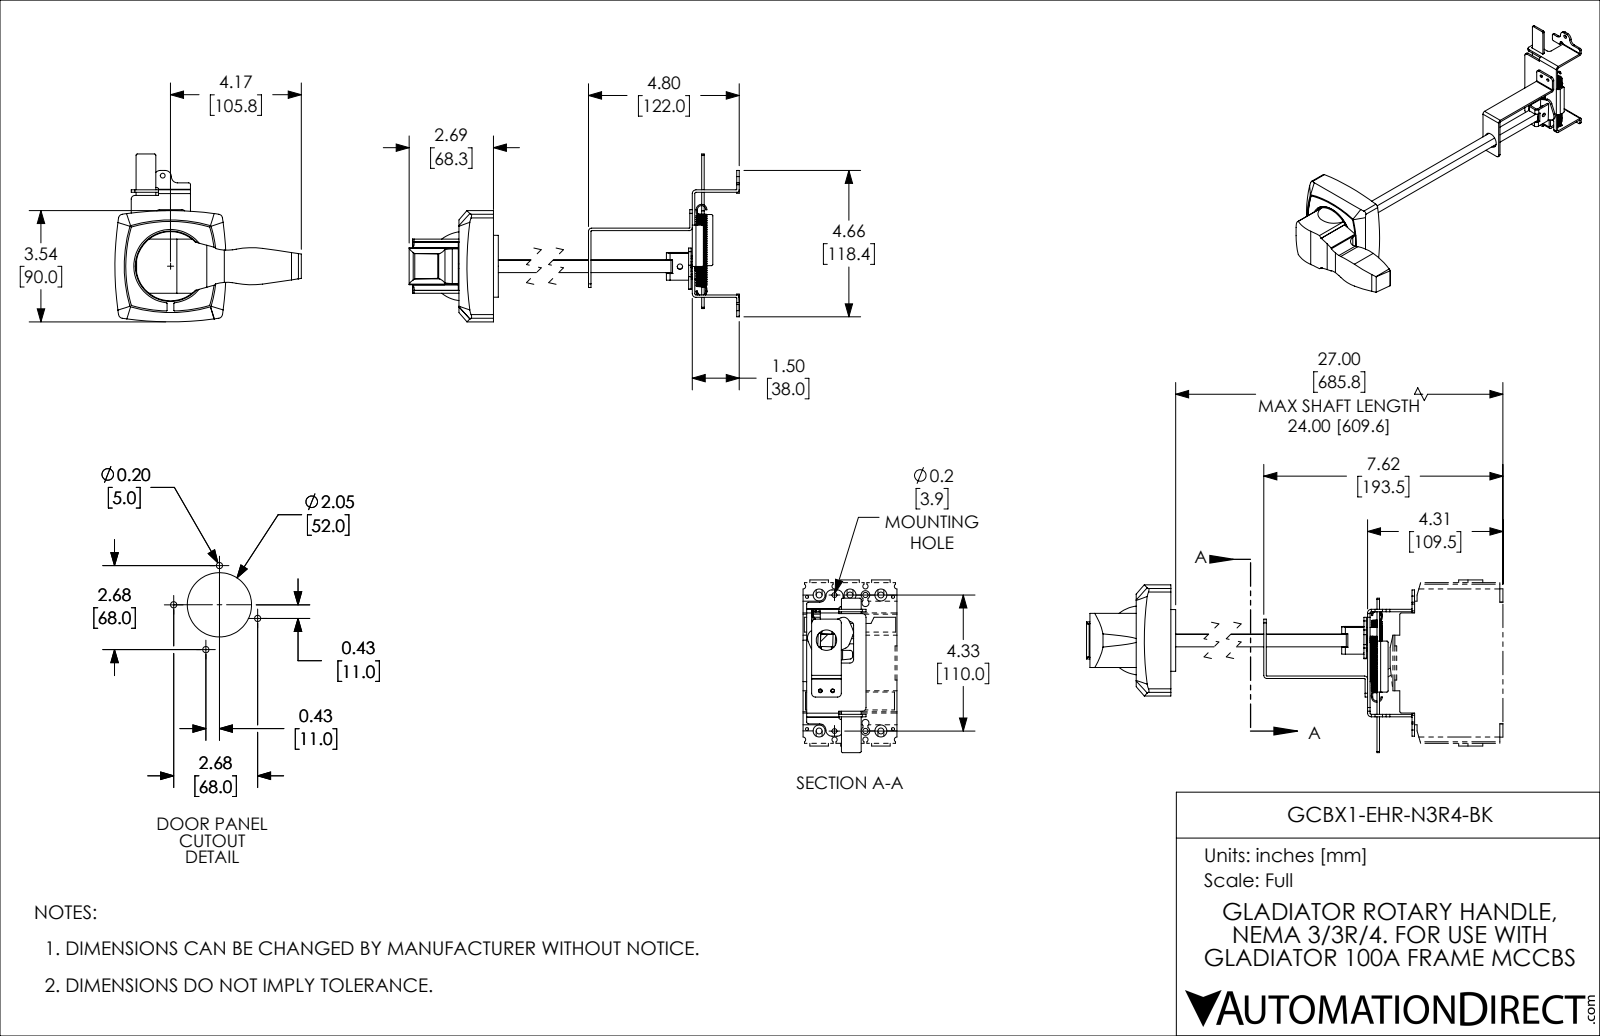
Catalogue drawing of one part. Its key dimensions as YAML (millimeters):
part_name: "GCBX1-EHR-N3R4-BK"
step_written_by: "SolidWorks 2021 (CONFIG_CONTROL_DESIGN)"
units: millimeters
bodies: {solids: 6, faces: 577, planar: 235, cylindrical: 242, other: 100}
overall_size: [404.87, 150.84, 135.79]
volume: 386745
surface_area: 95663
round_holes:
  - {diameter: 5, count: 4}
  - {diameter: 3, count: 3}
  - {diameter: 2.7, count: 2}
  - {diameter: 3.1, count: 2}
  - {diameter: 3.9, count: 2}
  - {diameter: 2.5, count: 1}
  - {diameter: 4.1, count: 1}
  - {diameter: 4.3, count: 1}
  - {diameter: 8.3, count: 1}
  - {diameter: 16.5, count: 1}
  - {diameter: 50, count: 1}
  - {diameter: 57, count: 1}
round_bosses_or_shafts:
  - {diameter: 2.5, count: 3}
  - {diameter: 59.5, count: 1}
  - {diameter: 50, count: 1}
  - {diameter: 9, count: 1}
  - {diameter: 8, count: 1}
  - {diameter: 7, count: 1}
  - {diameter: 6, count: 1}
  - {diameter: 4, count: 1}
partial_cylinders:
  - {radius: 3, count: 29}
  - {radius: 1, count: 23}
  - {radius: 0.5, count: 21}
  - {radius: 0.3, count: 12}
  - {radius: 1.5, count: 12}
  - {radius: 0.2, count: 10}
  - {radius: 5, count: 8}
  - {radius: 2, count: 6}
face_to_face_distances: [2, 7.6, 302.19, 330.69, 10, 10.01, 325.09, 4, 300.19, 332.69]
hole_center_spacings: [8.66, 14.86, 34, 35.74, 41.3, 68.88, 5.41, 8.33]
